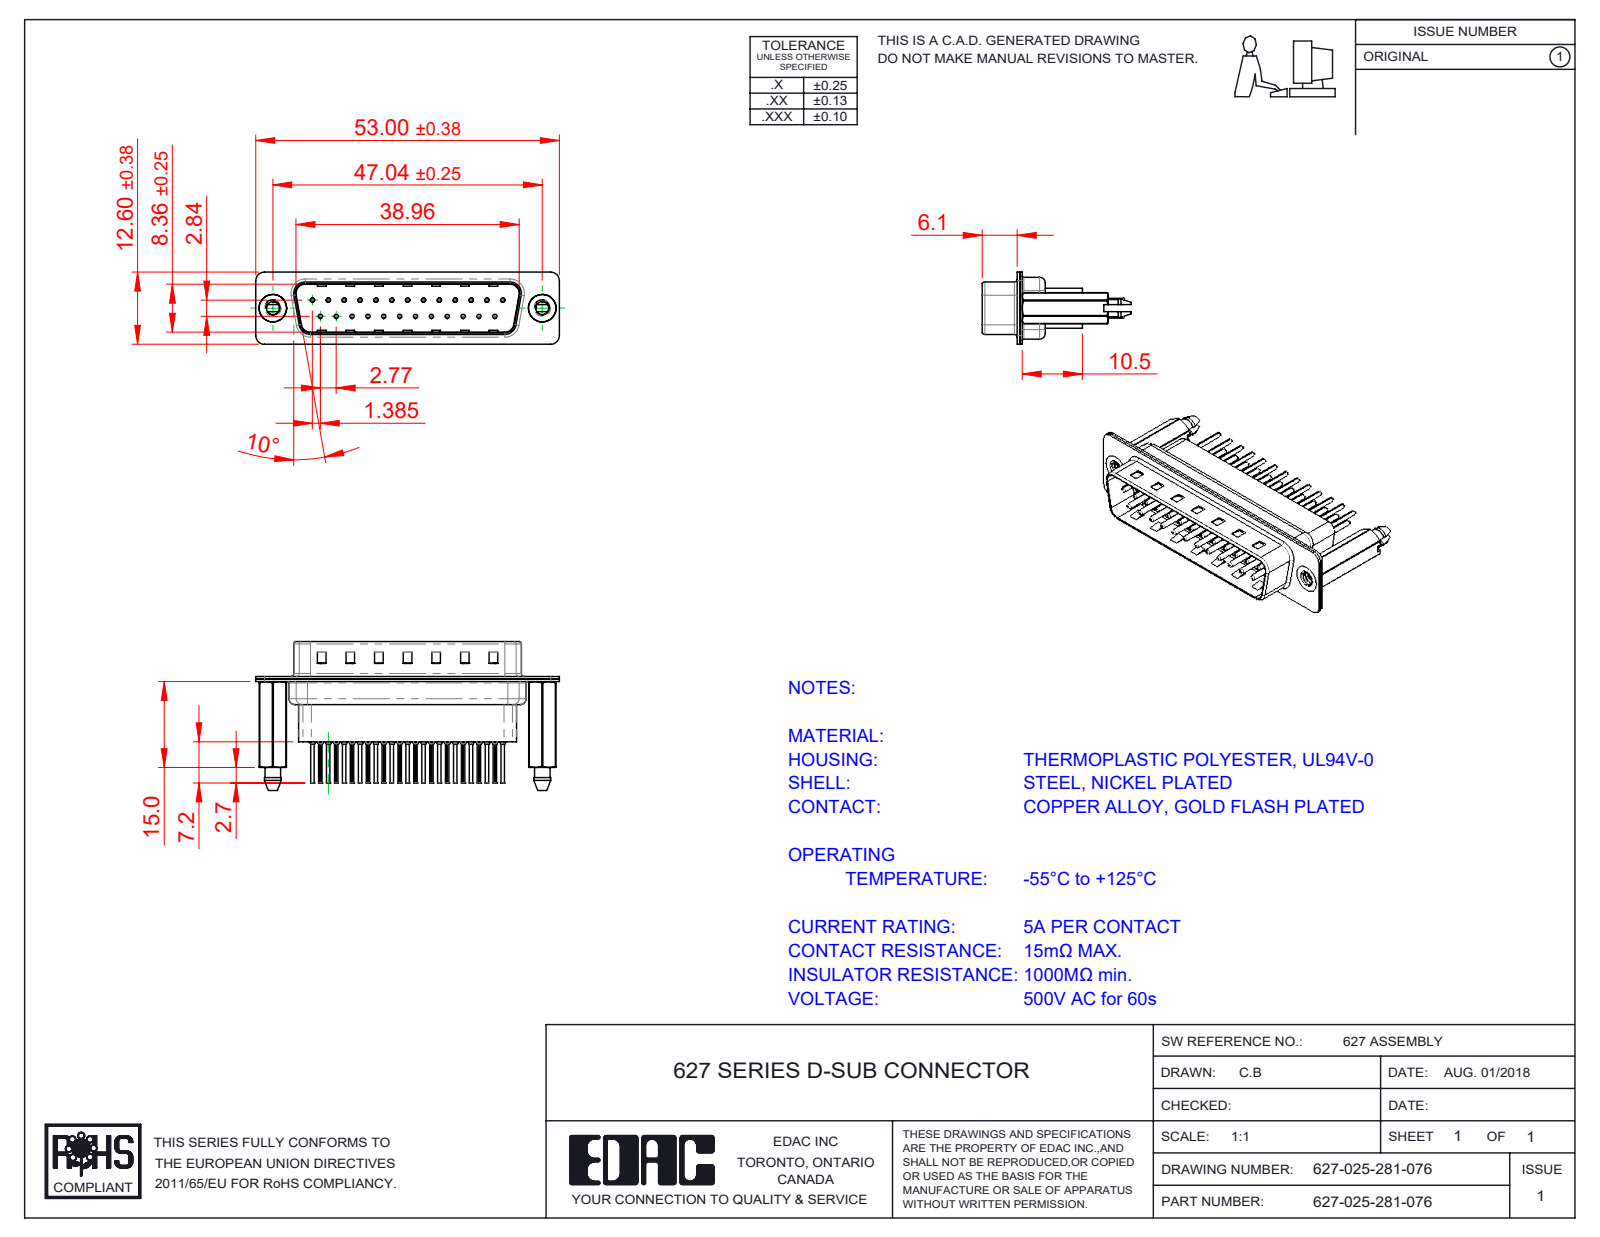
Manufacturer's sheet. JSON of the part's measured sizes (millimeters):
{"part_name": "627 Shell Front_25 Contacts; 627 Contact Row 2_61; 627 Shell Rear_25 Contacts; 627 Contact Row 1_61 (+3 more)", "step_written_by": "SolidWorks 2020 (CONFIG_CONTROL_DESIGN)", "units": "millimeters", "bodies": {"solids": 30, "faces": 2934, "planar": 803, "cylindrical": 1128, "other": 1003}, "overall_size": [53, 25.9, 12.6], "volume_mm3": 4205, "surface_area_mm2": 10831, "round_holes": [[0.2, 25], [0.35, 25], [1.1, 25], [1.6, 25], [2.26, 2], [4, 2], [4.8, 2]], "round_bosses_or_shafts": [[2, 25], [1.5, 25], [0.75, 25], [0.6, 25], [4.9, 2]], "partial_cylinders_radius": [[0.1, 50], [1.5, 18], [2, 12], [1.6, 10], [0.5, 8], [0.25, 4], [0.6, 4], [0.65, 4]], "face_to_face_distances": [0.4, 0.45, 0.82, 9.58, 0.68, 7.68, 1.5, 0.9, 1.08, 8.08], "hole_center_spacings": [3.16, 8.31, 2.77, 5.54, 11.08, 16.62, 5.03, 5.04]}
